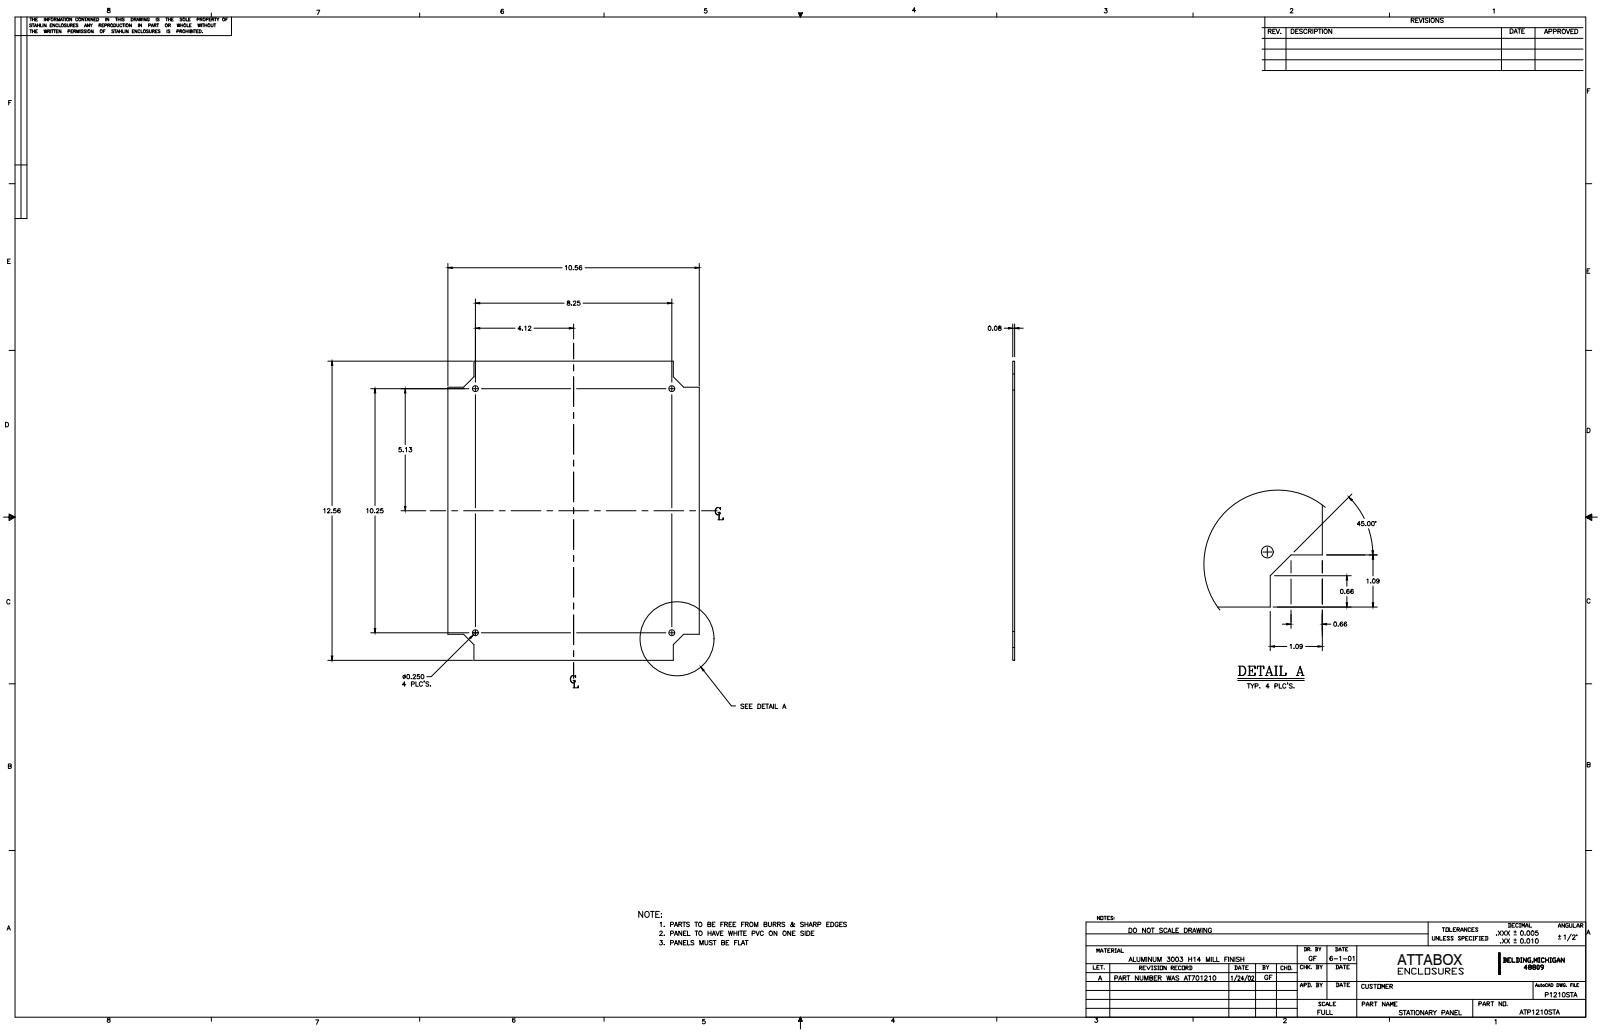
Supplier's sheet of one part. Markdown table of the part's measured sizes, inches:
| quantity | value |
| --- | --- |
| part name | P1210STAL |
| STEP written by | Autodesk Inventor 11 (AUTOMOTIVE_DESIGN) |
| units | inches |
| bodies | 1 solid, 22 faces (18 planar, 4 cylindrical, 0 other) |
| overall size | 12.563 × 10.563 × 0.08 |
| volume | 10.25 in³ |
| surface area | 260 in² |
| round holes (diameter × count) | 0.25 × 4 |
| main face-to-face distances | 0.08, 10.562, 12.562, 1.094, 9.468, 11.468, 8.374, 10.374, 13.873 |
| hole center spacings | 8.25, 10.25, 13.157, 13.158 |
